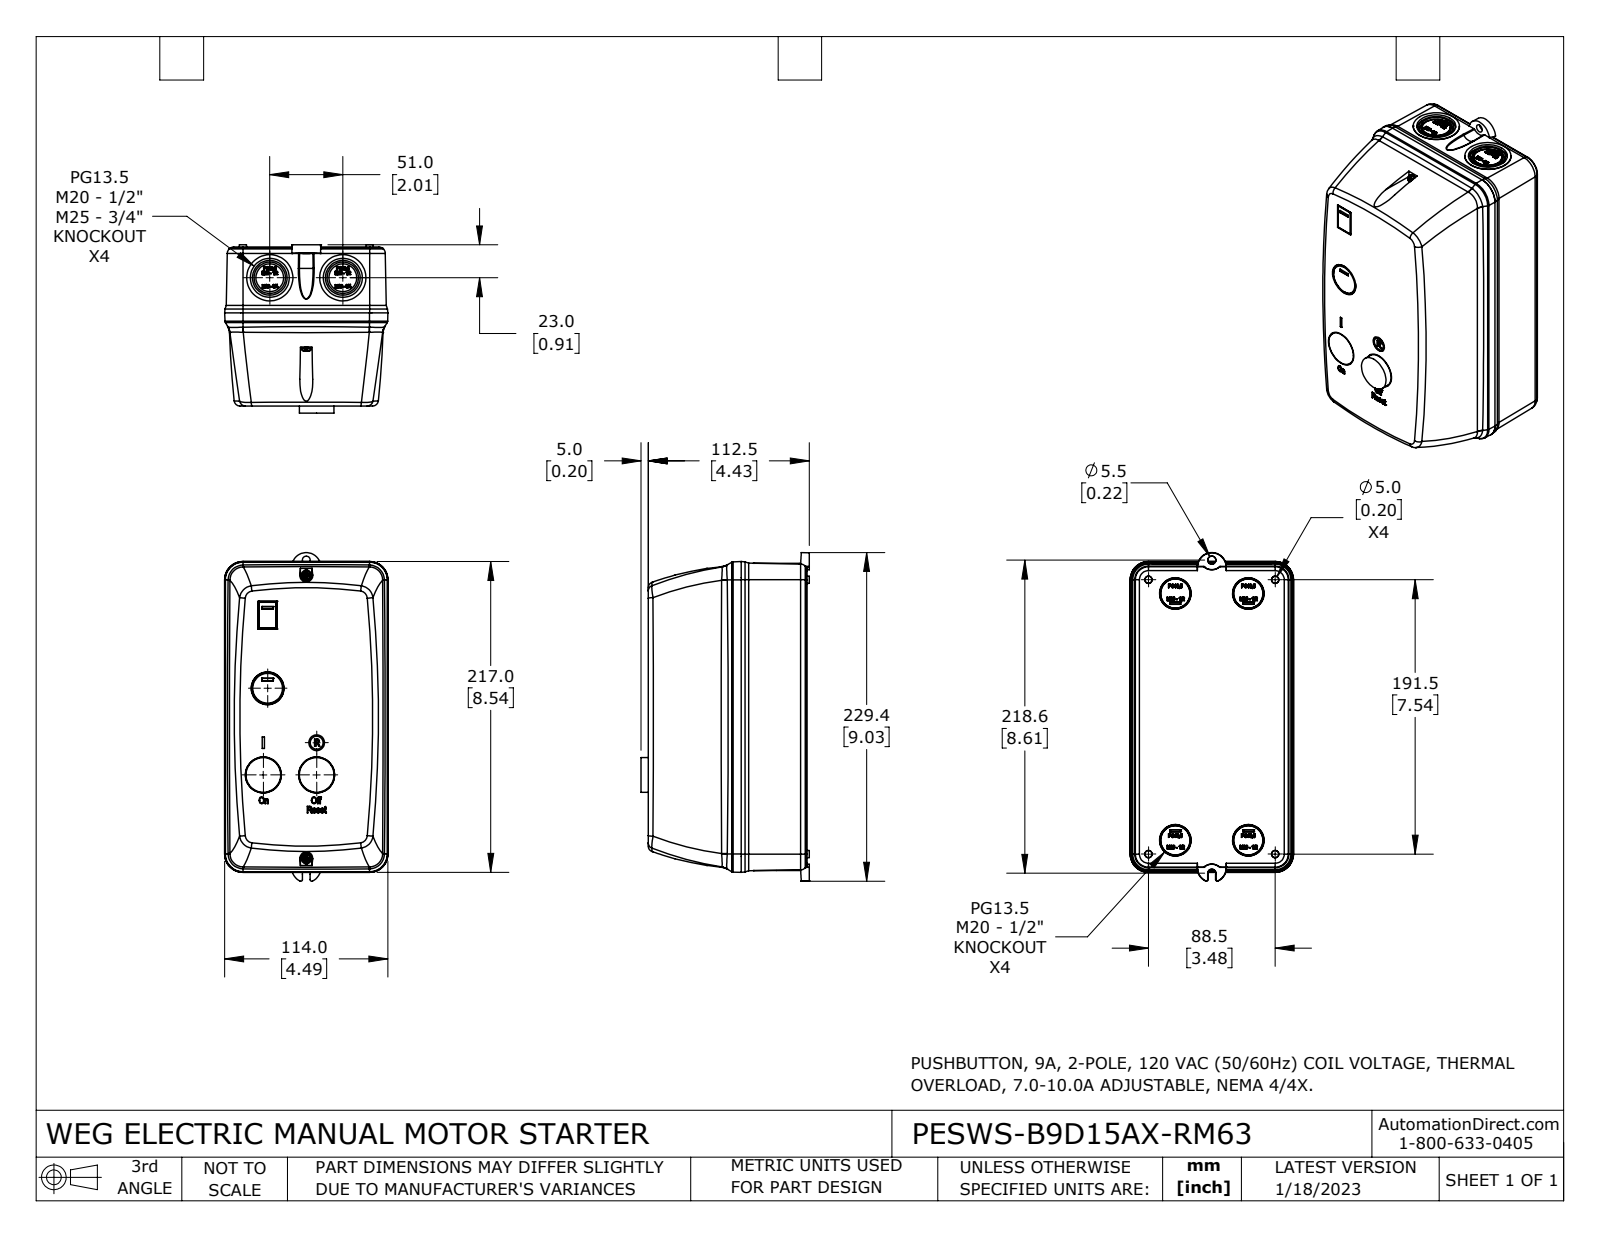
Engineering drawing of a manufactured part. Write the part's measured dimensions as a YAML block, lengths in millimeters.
part_name: "PESWS-B9D15AX-RM63"
step_written_by: "SolidWorks 2021 (CONFIG_CONTROL_DESIGN)"
units: millimeters
bodies: {solids: 6, faces: 2195, planar: 1110, cylindrical: 92, other: 993}
overall_size: [229.44, 117.5, 114.01]
volume: 2457000
surface_area: 166196
round_holes:
  - {diameter: 4.4, count: 2}
  - {diameter: 21.91, count: 2}
  - {diameter: 27.24, count: 2}
  - {diameter: 5.5, count: 1}
  - {diameter: 11, count: 1}
round_bosses_or_shafts:
  - {diameter: 32.26, count: 2}
  - {diameter: 24.25, count: 2}
  - {diameter: 24.2, count: 2}
  - {diameter: 19.37, count: 2}
  - {diameter: 7, count: 2}
  - {diameter: 3, count: 2}
  - {diameter: 9, count: 1}
partial_cylinders:
  - {radius: 2, count: 4}
  - {radius: 4.61, count: 4}
  - {radius: 9.54, count: 4}
  - {radius: 6.54, count: 2}
  - {radius: 7.54, count: 2}
  - {radius: 2.08, count: 1}
  - {radius: 2.17, count: 1}
  - {radius: 2.75, count: 1}
face_to_face_distances: [46, 65, 111, 0.5, 110.5, 45.5, 110, 1, 109.5, 64]
hole_center_spacings: [10.5, 51, 81.32, 117.22, 127.71, 198, 208.5]
